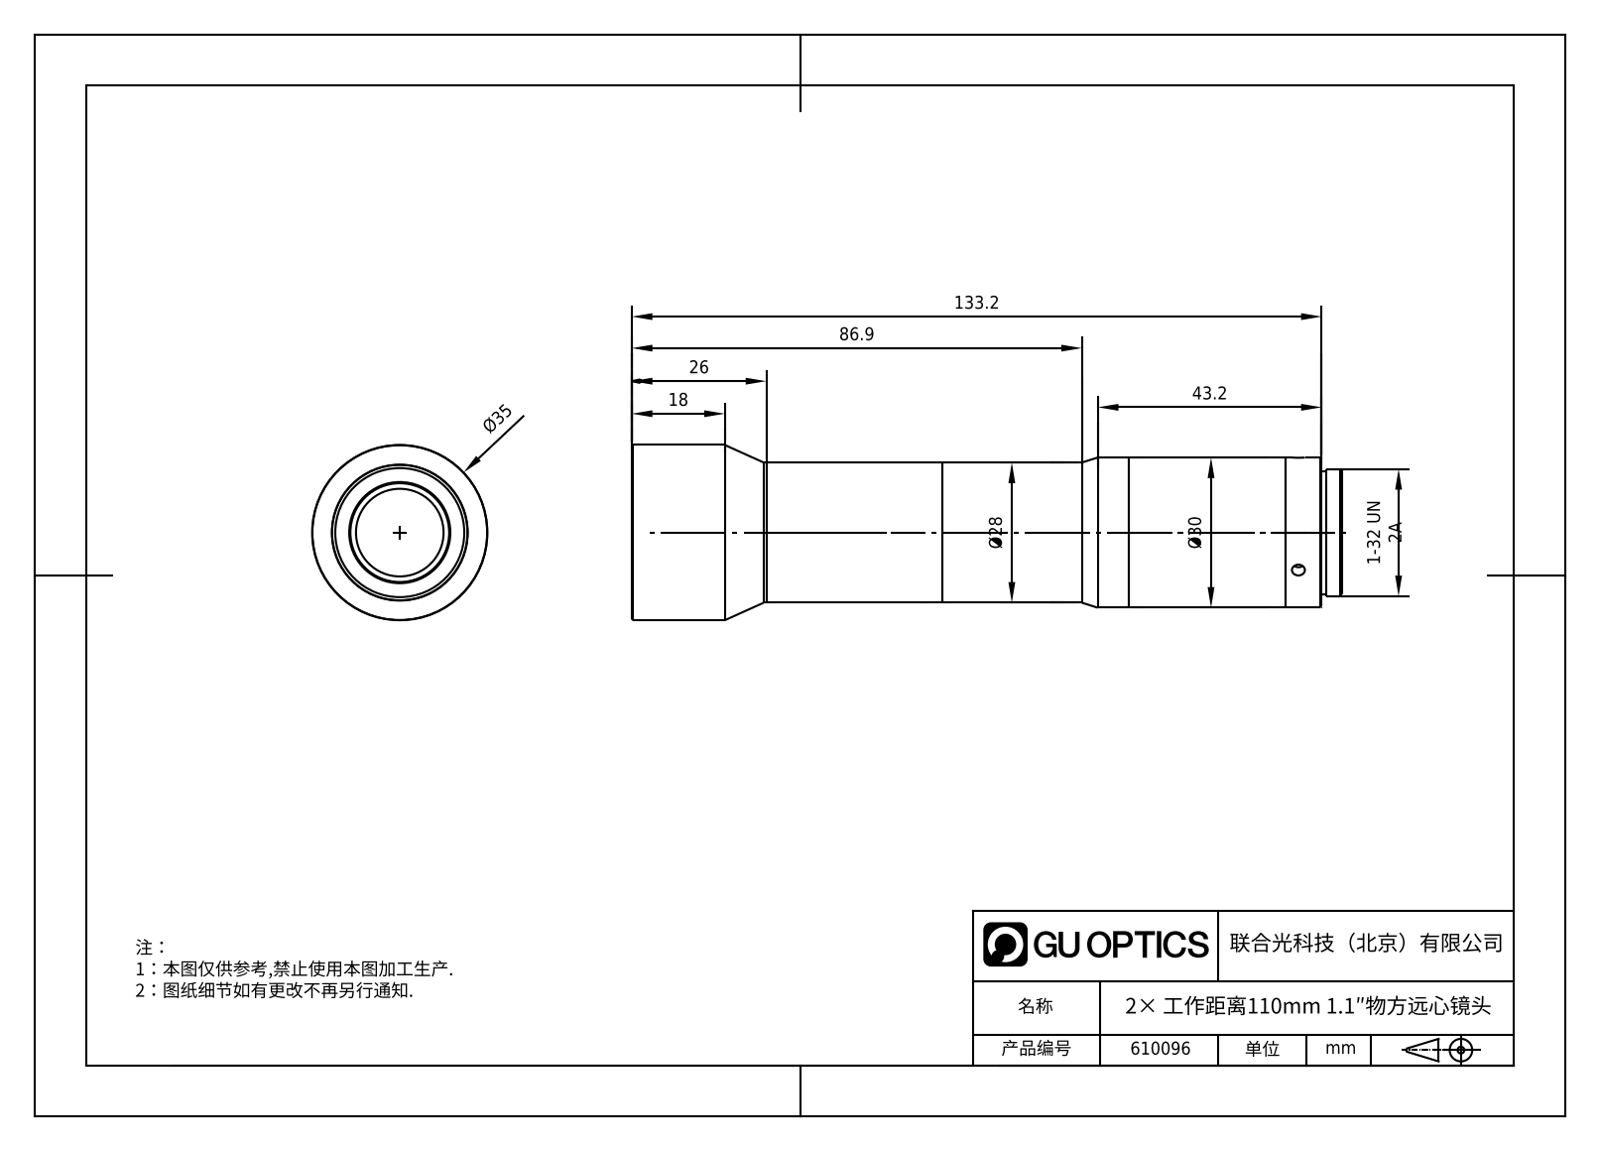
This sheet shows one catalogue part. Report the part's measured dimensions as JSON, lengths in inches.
{"part_name": "WWK20-110-111", "step_written_by": "SolidWorks 2012 (CONFIG_CONTROL_DESIGN)", "units": "inches", "bodies": {"solids": 1, "faces": 46, "planar": 5, "cylindrical": 22, "other": 19}, "overall_size": [5.398, 1.378, 1.378], "volume_in3": 5.754, "surface_area_in2": 23.07, "round_holes": [[0.098, 3], [0.768, 1], [0.906, 1], [1.24, 1]], "round_bosses_or_shafts": [[1.378, 1], [1.181, 1], [1.102, 1], [1, 1], [0.969, 1]], "face_to_face_distances": [0.154, 5.398, 5.244, 0.122, 0.031, 5.276]}
